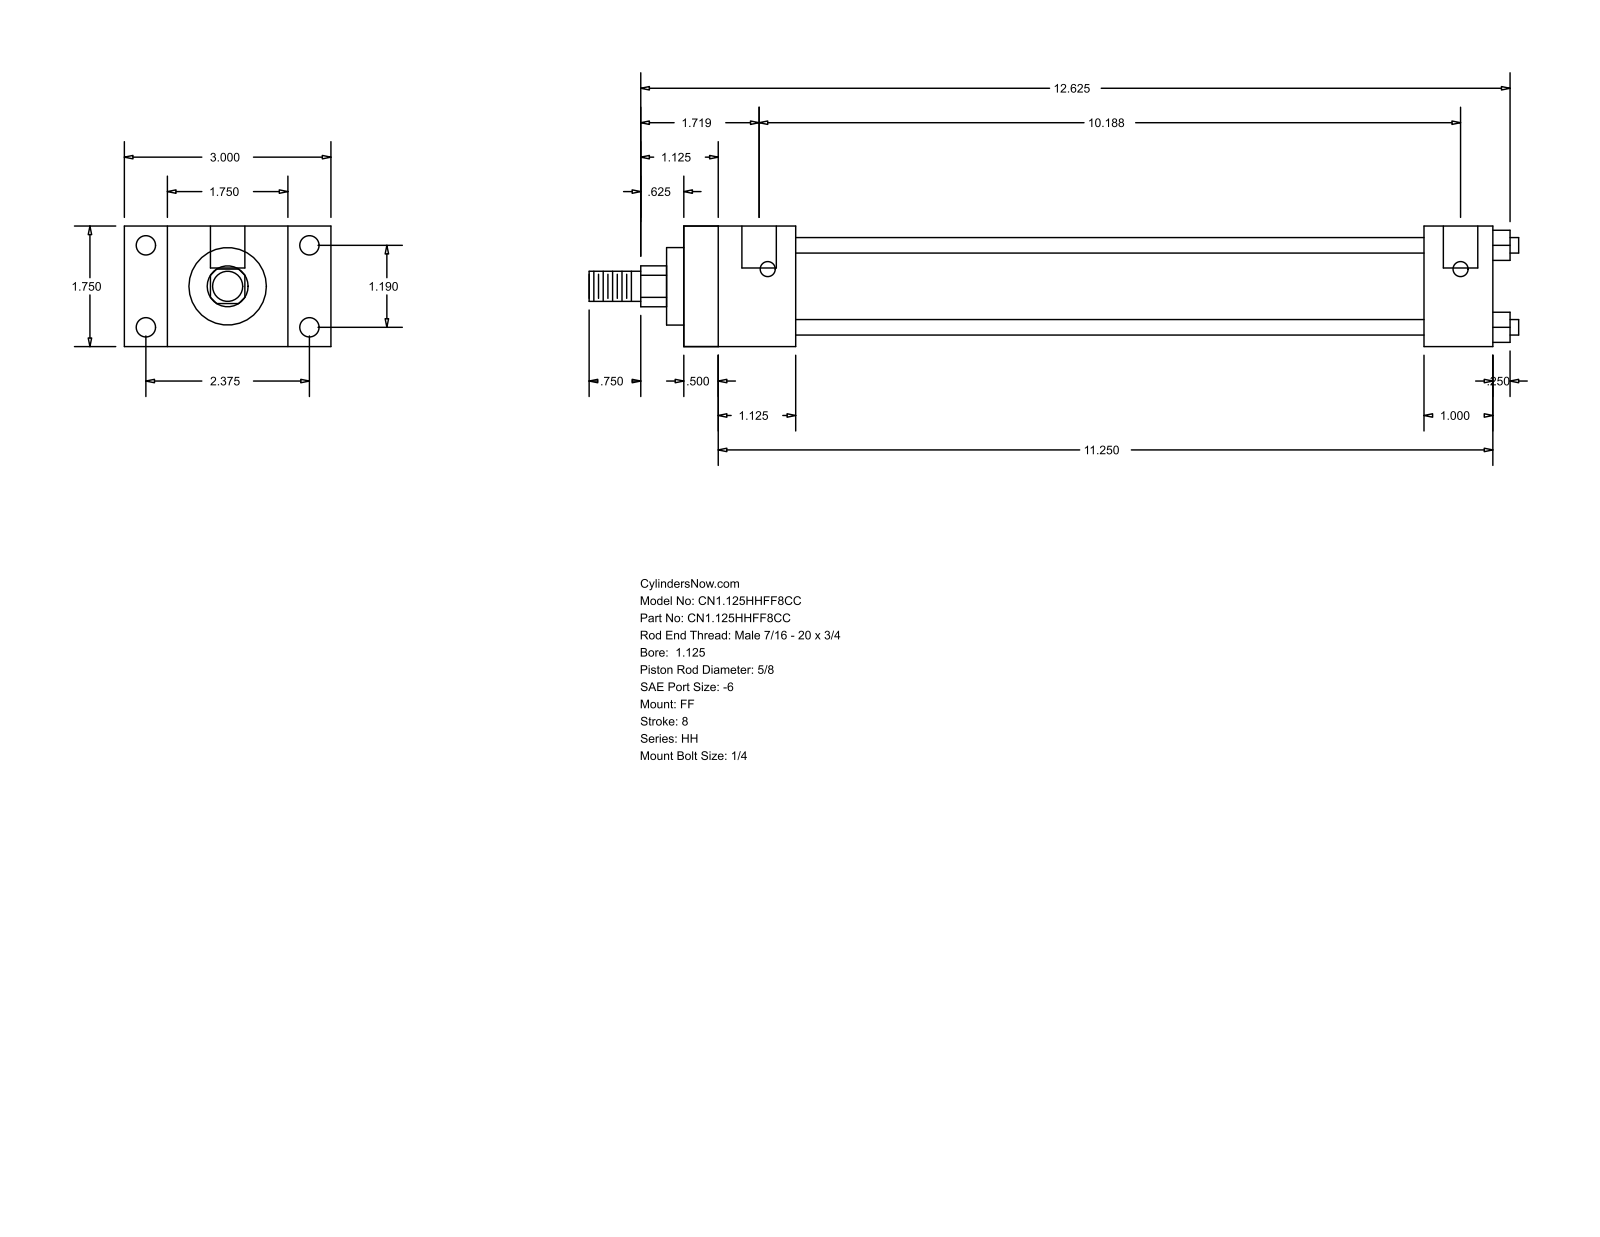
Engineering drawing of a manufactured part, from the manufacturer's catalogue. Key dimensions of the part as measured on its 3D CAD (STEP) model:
Part name (STEP PRODUCT): HH_FF__0112_0.625
STEP written by: GSSL Pune (CONFIG_CONTROL_DESIGN)
Units: millimetres
Bodies: 0 solids, 92 faces (64 planar, 28 cylindrical, 0 other)
Overall size (bounding box): 342.9 × 76.2 × 44.45
Round holes (diameter × count): ⌀5.56 ×4, ⌀7.14 ×4, ⌀12.7 ×2
Round bosses / shafts (diameter × count): ⌀5.71 ×4, ⌀34.92 ×1, ⌀28.57 ×1, ⌀15.88 ×1, ⌀11.11 ×1
Partial cylindrical surfaces — rounded edges, fillets, slot ends (radius × count): R7.54 ×1
Main face-to-face distances: 44.46, 298.44, 12.69, 285.75, 15.87, 28.58, 60.33, 41.27, 273.05, 260.36
Hole centre spacings: 30.22, 60.32, 67.47, 255.59, 3.17, 258.76
